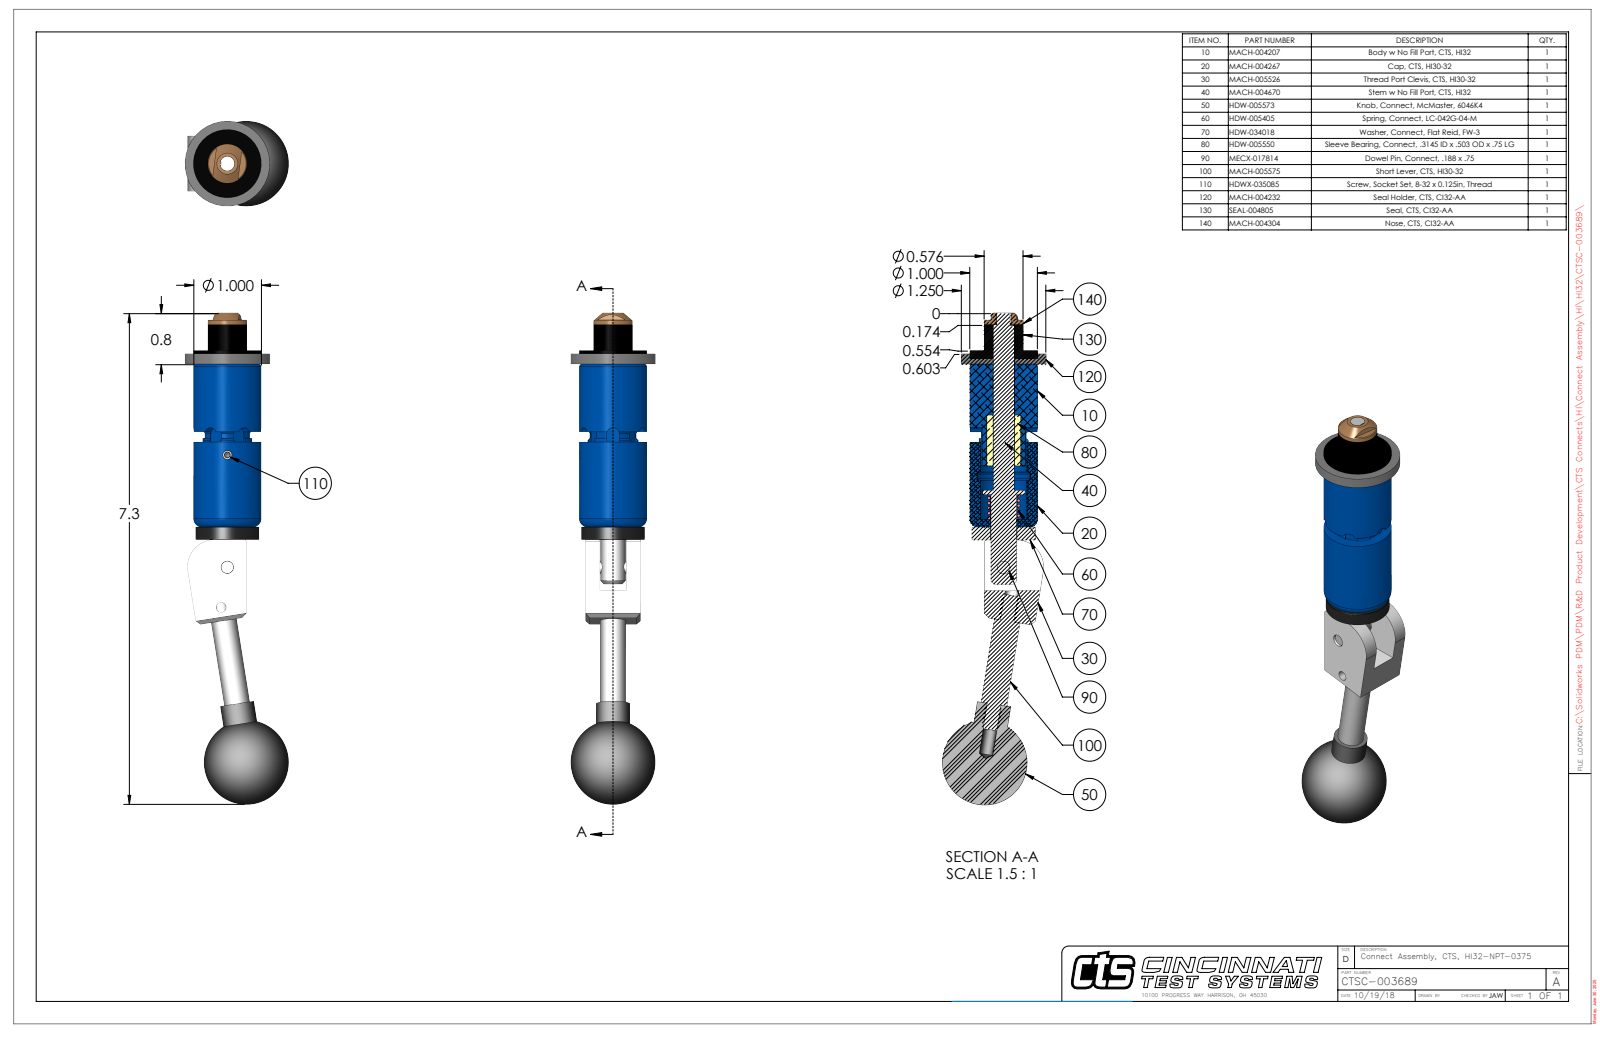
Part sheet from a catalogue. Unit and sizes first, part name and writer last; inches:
Units: inches
Overall size (bounding box): 7.256 × 1.53 × 1.25
Round holes (diameter × count): ⌀0.201 ×2, ⌀0.136 ×1, ⌀0.15 ×1, ⌀0.189 ×1, ⌀0.213 ×1, ⌀0.31 ×1, ⌀0.314 ×1, ⌀0.316 ×1, ⌀0.385 ×1, ⌀0.392 ×1, ⌀0.688 ×1
Round bosses / shafts (diameter × count): ⌀0.25 ×2, ⌀0.201 ×2, ⌀1.25 ×1, ⌀1 ×1, ⌀0.936 ×1, ⌀0.578 ×1, ⌀0.576 ×1, ⌀0.5 ×1
Partial cylindrical surfaces — rounded edges, fillets, slot ends (radius × count): R0.093 ×6, R0.029 ×2, R0.375 ×1, R0.4 ×1, R0.446 ×1
Main face-to-face distances: 0.081, 0.21, 0.602, 2.485, 2.404, 0.812, 2.672, 2.591, 0.187, 0.391
Hole centre spacings: 0.599, 1.658, 2.252
Volume: 4.099 in³ · Surface area: 35.73 in²
Bodies: 9 solids, 277 faces (107 planar, 112 cylindrical, 58 other)
Part name (STEP PRODUCT): CTSC-003689
STEP written by: SolidWorks 2023 (AUTOMOTIVE_DESIGN)
